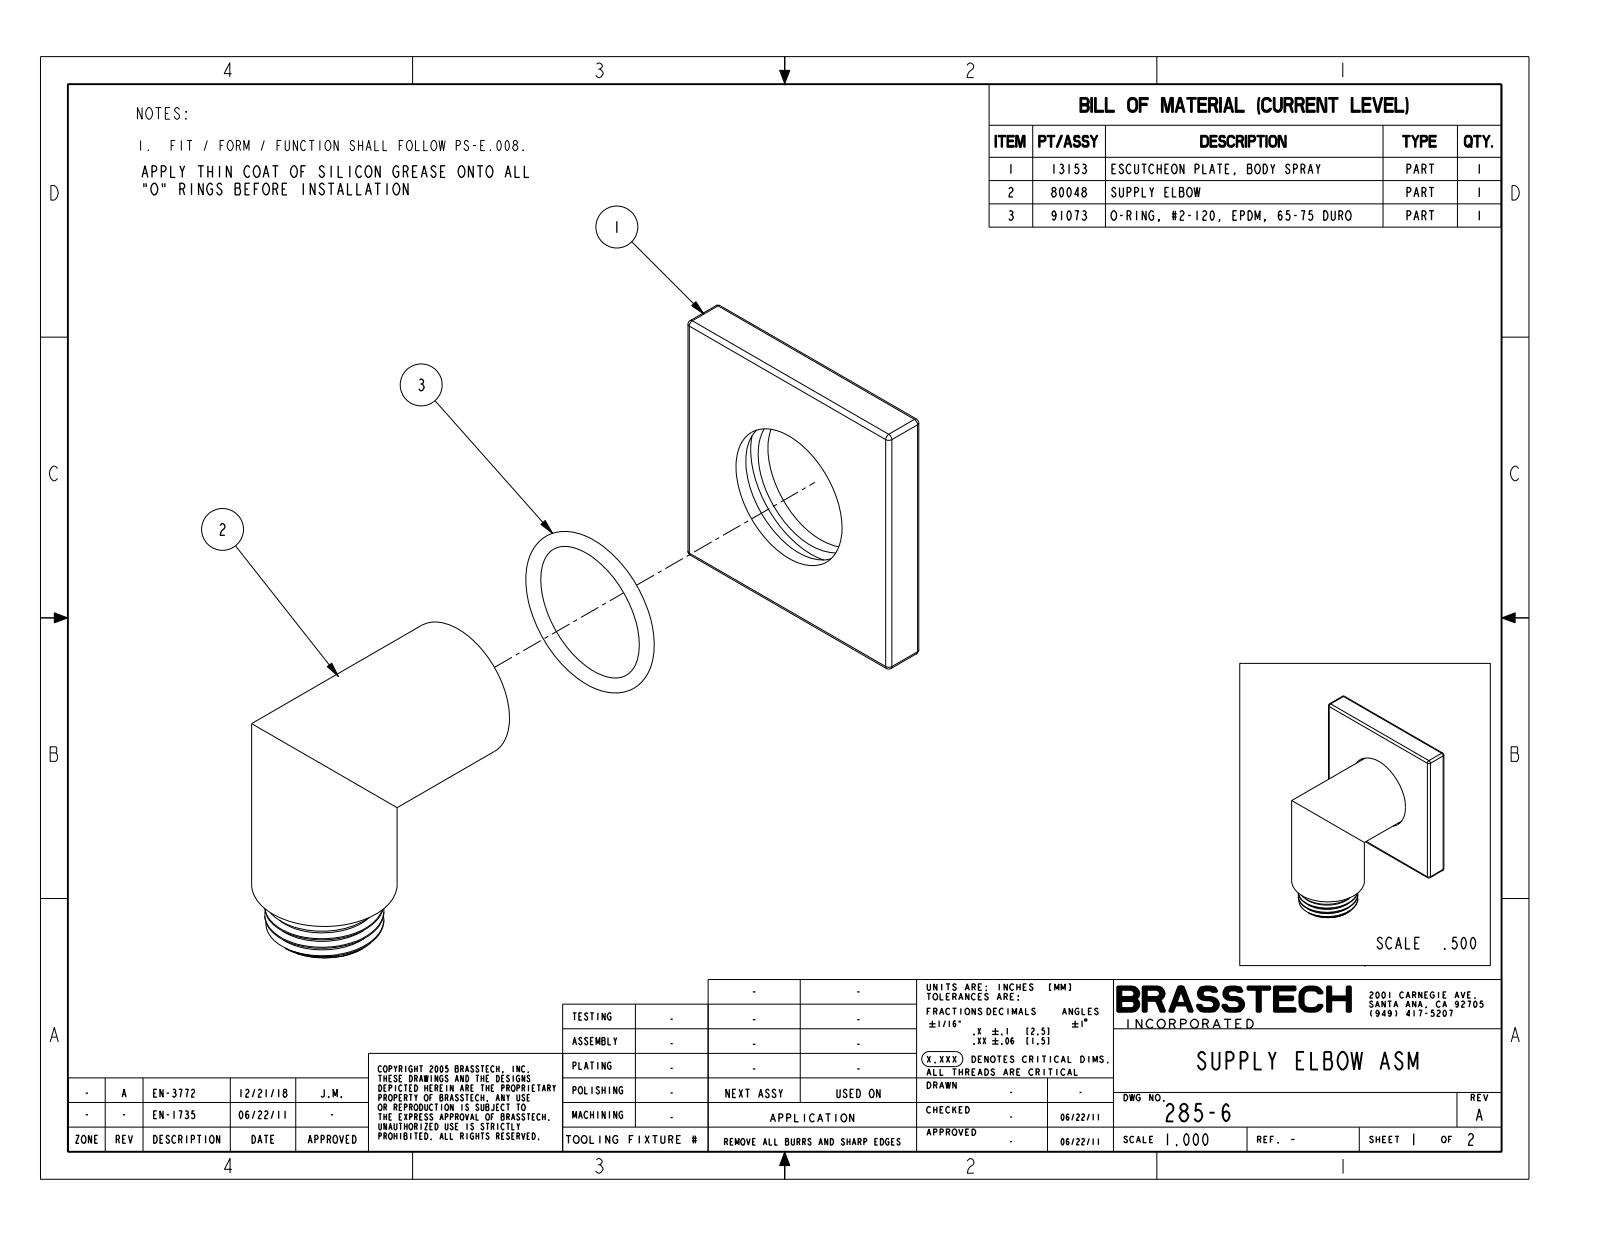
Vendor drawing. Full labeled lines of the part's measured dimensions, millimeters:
Part name (STEP PRODUCT): 285-6
STEP written by: CREO PARAMETRIC BY PTC INC, 2019352 (CONFIG_CONTROL_DESIGN)
Units: millimetres
Bodies: 1 solid, 40 faces (8 planar, 18 cylindrical, 14 other)
Overall size (bounding box): 59.5 × 50 × 45.7
Volume: 47 950 mm³ · Surface area: 11 320 mm²
Round bosses / shafts (diameter × count): ⌀25.4 ×2, ⌀20.8 ×1, ⌀18.5 ×1
Partial cylindrical surfaces — rounded edges, fillets, slot ends (radius × count): R1 ×8
Main face-to-face distances: 7.9, 50, 9.4, 59.5, 9.1, 0.4, 50.4
